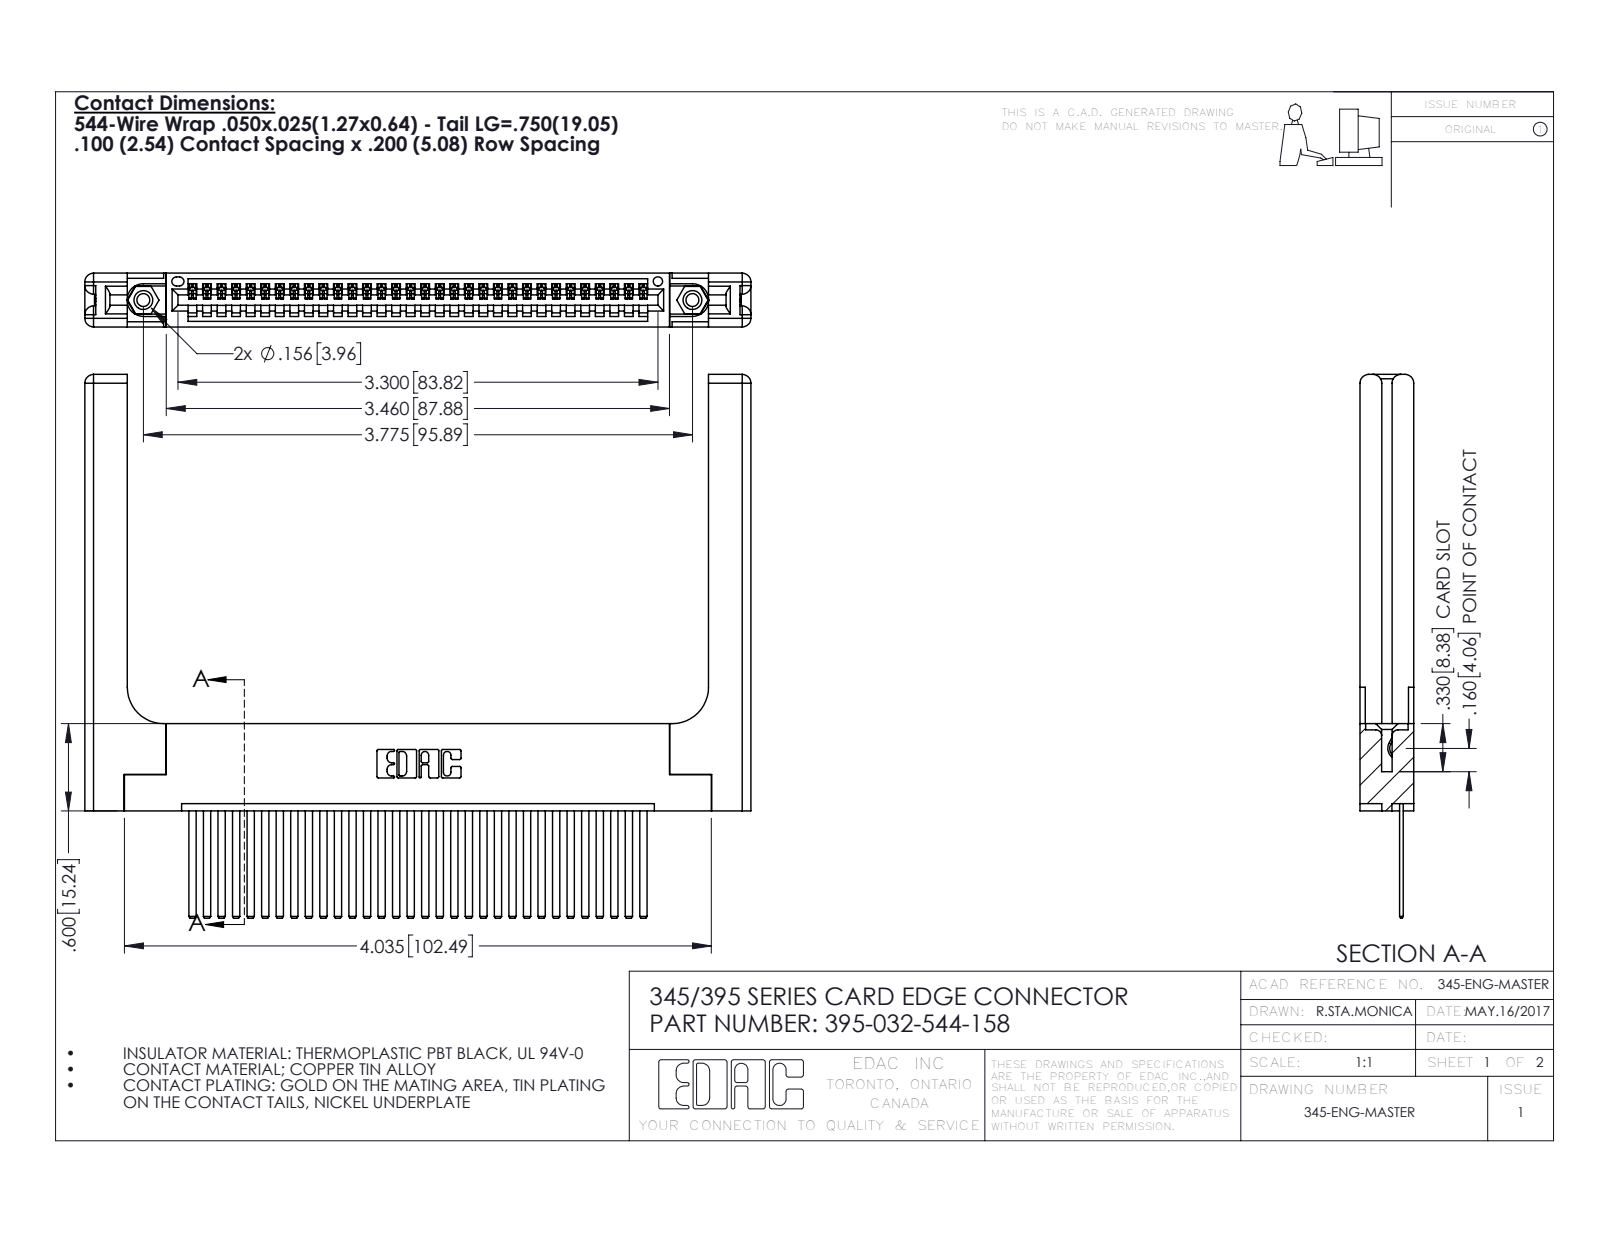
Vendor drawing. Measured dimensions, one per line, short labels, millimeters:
name: 345-250-001_345-250-001-102; 395-032-544-158; 345-292-001_345-293-144; 345 Part_Flush Mounting Lugs - 0.156 Dia-TH (+1 more)
written by: SolidWorks 2016 (CONFIG_CONTROL_DESIGN)
unit: mm
bodies: 37 solids, 2046 faces (1380 planar, 606 cylindrical, 60 other)
size: 116.3 × 94.9 × 9.4
volume: 19 840 mm³; area: 21 350 mm²
holes: 2× ⌀2.3, 2× ⌀3.2, 2× ⌀4, 1× ⌀1.6
bosses: 2× ⌀3.9
rounds: 64× R0.2, 22× R0.3, 16× R1.5, 6× R0.2, 6× R0.8, 3× R0.7, 2× R0.8, 2× R0.8
face distances: 1.8, 7.6, 9.4, 2.5, 6.9, 0.6, 5.1, 3.8, 3.8, 2
hole spacings: 6.9, 89.9, 95.9
